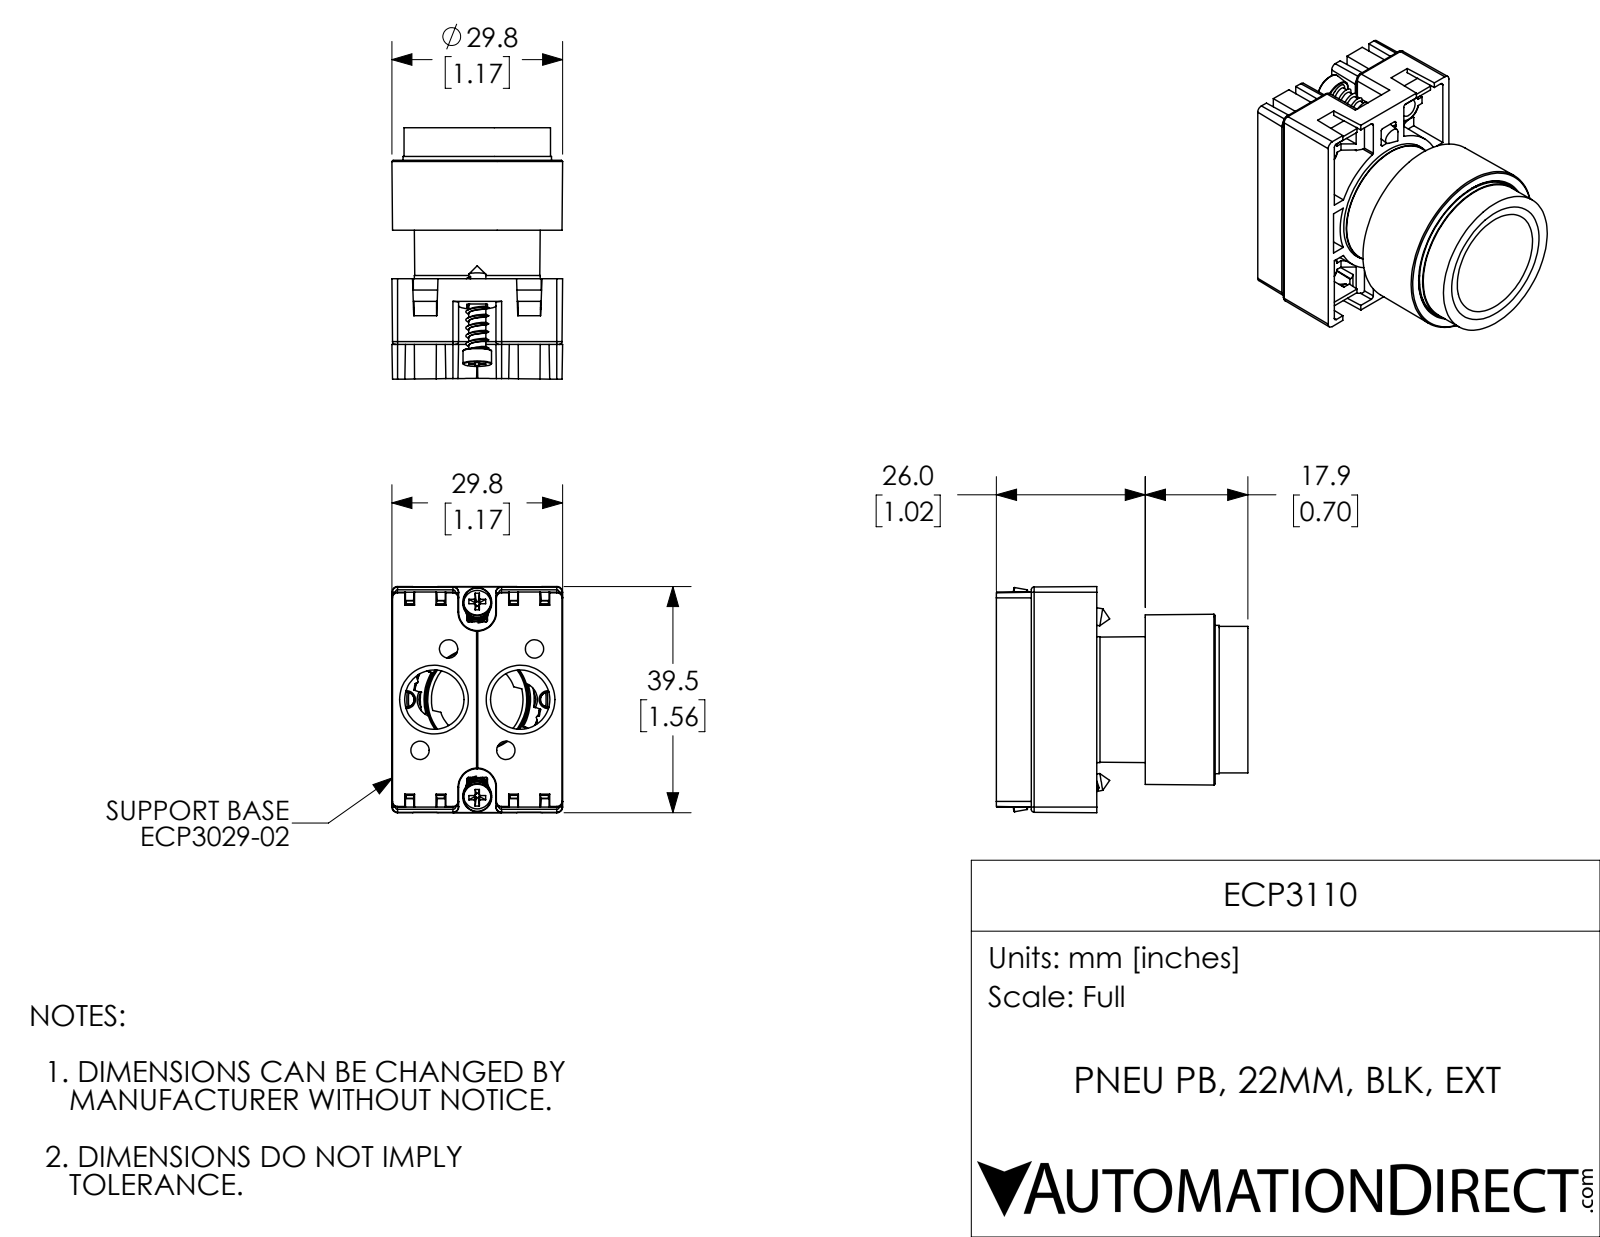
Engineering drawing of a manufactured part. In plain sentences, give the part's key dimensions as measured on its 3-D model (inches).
The part is named "ECP3110". Its 3-D file was written by "SolidWorks 2017 (AUTOMOTIVE_DESIGN)". It is 7 solids with 781 faces: 364 planar, 133 cylindrical and 284 other. Overall it measures 1.728 by 1.555 by 1.173 inches. Its volume is 1.025 cubic inches and its surface area 29.57 square inches. Round holes: 4 of diameter 0.081, 2 of diameter 0.407, 1 of diameter 0.697, 1 of diameter 0.732. Round bosses or shafts: 2 of diameter 0.197, 2 of diameter 0.118, 1 of diameter 1.02, 1 of diameter 1.008, 1 of diameter 0.866. Partial cylindrical surfaces (rounded edges, fillets, slot ends): 18 of radius 0.02, 8 of radius 0.006, 8 of radius 0.012, 4 of radius 0.008, 4 of radius 0.039, 2 of radius 0.008, 2 of radius 0.118, 2 of radius 0.128. The main face-to-face distances are 1.261, 0.177, 0.067, 0.715, 0.962, 0.811, 0.451, 0.587, 0.528, 0.519. The hole center spacings are 0.304, 0.541, 0.817, 0.295, 0.472, 0.972, 1.081, 0.591.
